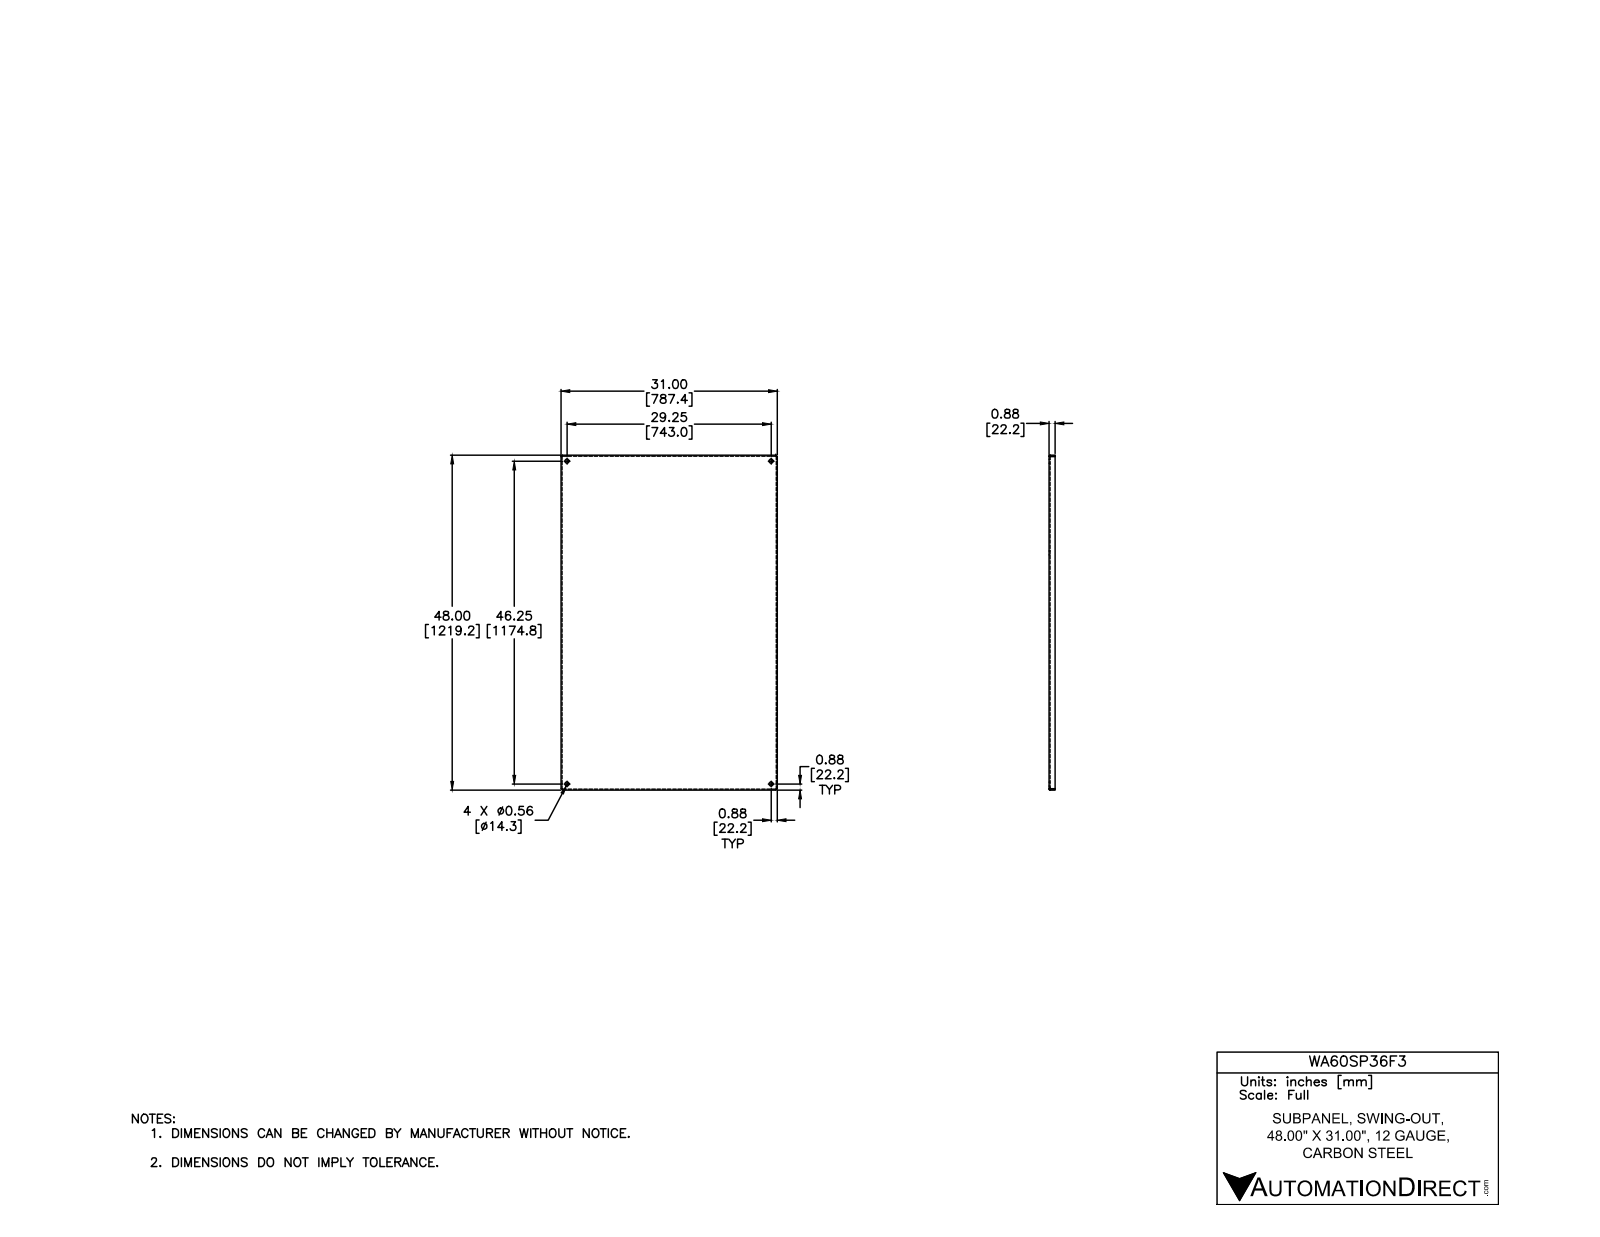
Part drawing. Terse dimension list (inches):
name: WA60SP24F3-WA90SP36F4
written by: Autodesk Inventor 2012 (AUTOMOTIVE_DESIGN)
unit: in
bodies: 1 solid, 42 faces (22 planar, 12 cylindrical, 8 other)
size: 48 × 31 × 0.875
volume: 150.4 in³; area: 3 224 in²
holes: 4× ⌀0.563
rounds: 4× R0.031, 4× R0.125
face distances: 0.094, 30.906, 47.906, 31, 30.813, 48, 47.813, 0.781, 0.875, 0.16
hole spacings: 29.25, 46.25, 54.723
